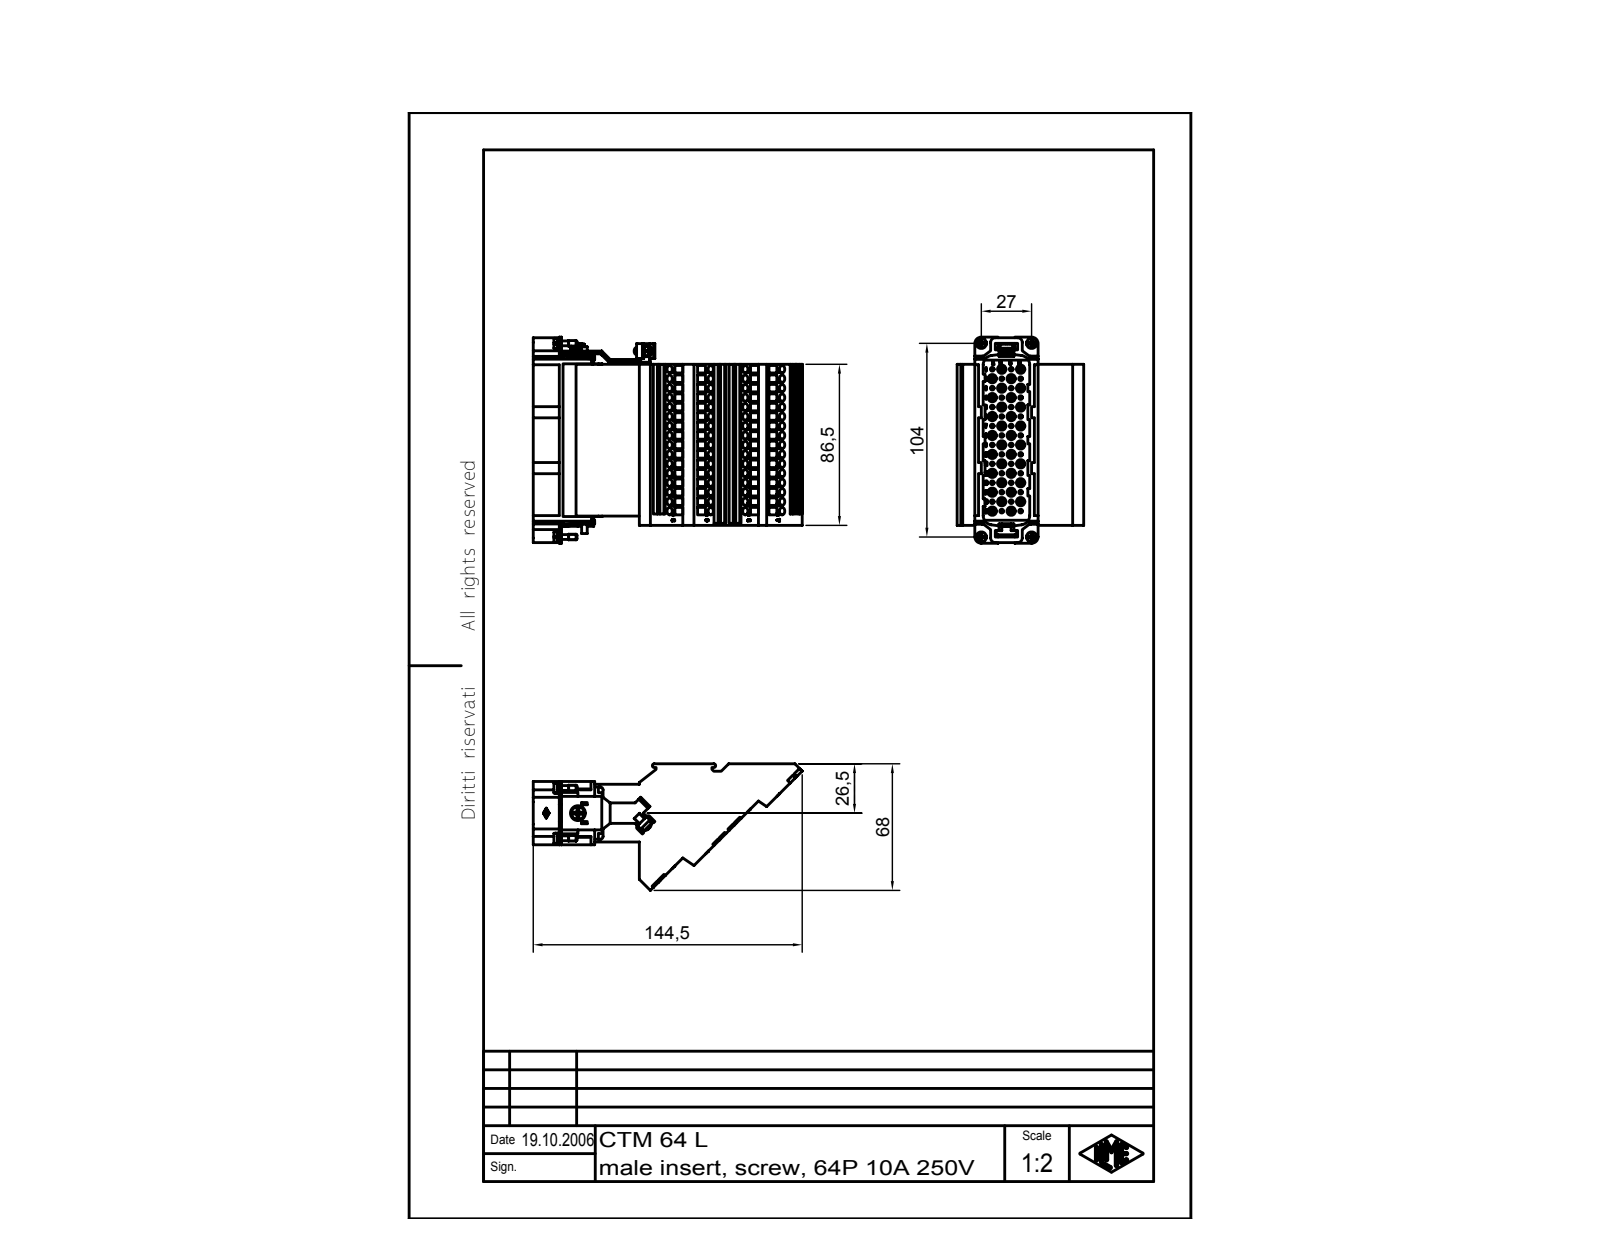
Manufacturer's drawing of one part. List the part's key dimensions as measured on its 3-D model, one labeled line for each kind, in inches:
Part name (STEP PRODUCT): CTM 64 L
STEP written by: Autodesk Inventor 7 (AUTOMOTIVE_DESIGN)
Units: inches
Bodies: 3 solids, 3253 faces (1689 planar, 448 cylindrical, 1116 other)
Overall size (bounding box): 5.689 × 4.358 × 2.677
Volume: 23.49 in³ · Surface area: 142.7 in²
Round holes (diameter × count): ⌀0.157 ×64, ⌀0.098 ×32, ⌀0.128 ×1
Round bosses / shafts (diameter × count): ⌀0.079 ×64, ⌀0.177 ×32, ⌀0.217 ×2, ⌀0.209 ×2, ⌀0.118 ×2, ⌀0.102 ×2, ⌀0.315 ×1, ⌀0.276 ×1
Partial cylindrical surfaces — rounded edges, fillets, slot ends (radius × count): R0.004 ×14, R0.039 ×6, R0.098 ×4, R0.197 ×4, R0.008 ×2, R0.059 ×2, R0.138 ×2
Main face-to-face distances: 0.02, 0.059, 1.22, 0.098, 0.433, 0.079, 0.236, 1.654, 0.118, 1.102
Hole centre spacings: 0.4, 0.632, 0.283, 0.8, 1.02, 1.2, 0.2, 0.566
